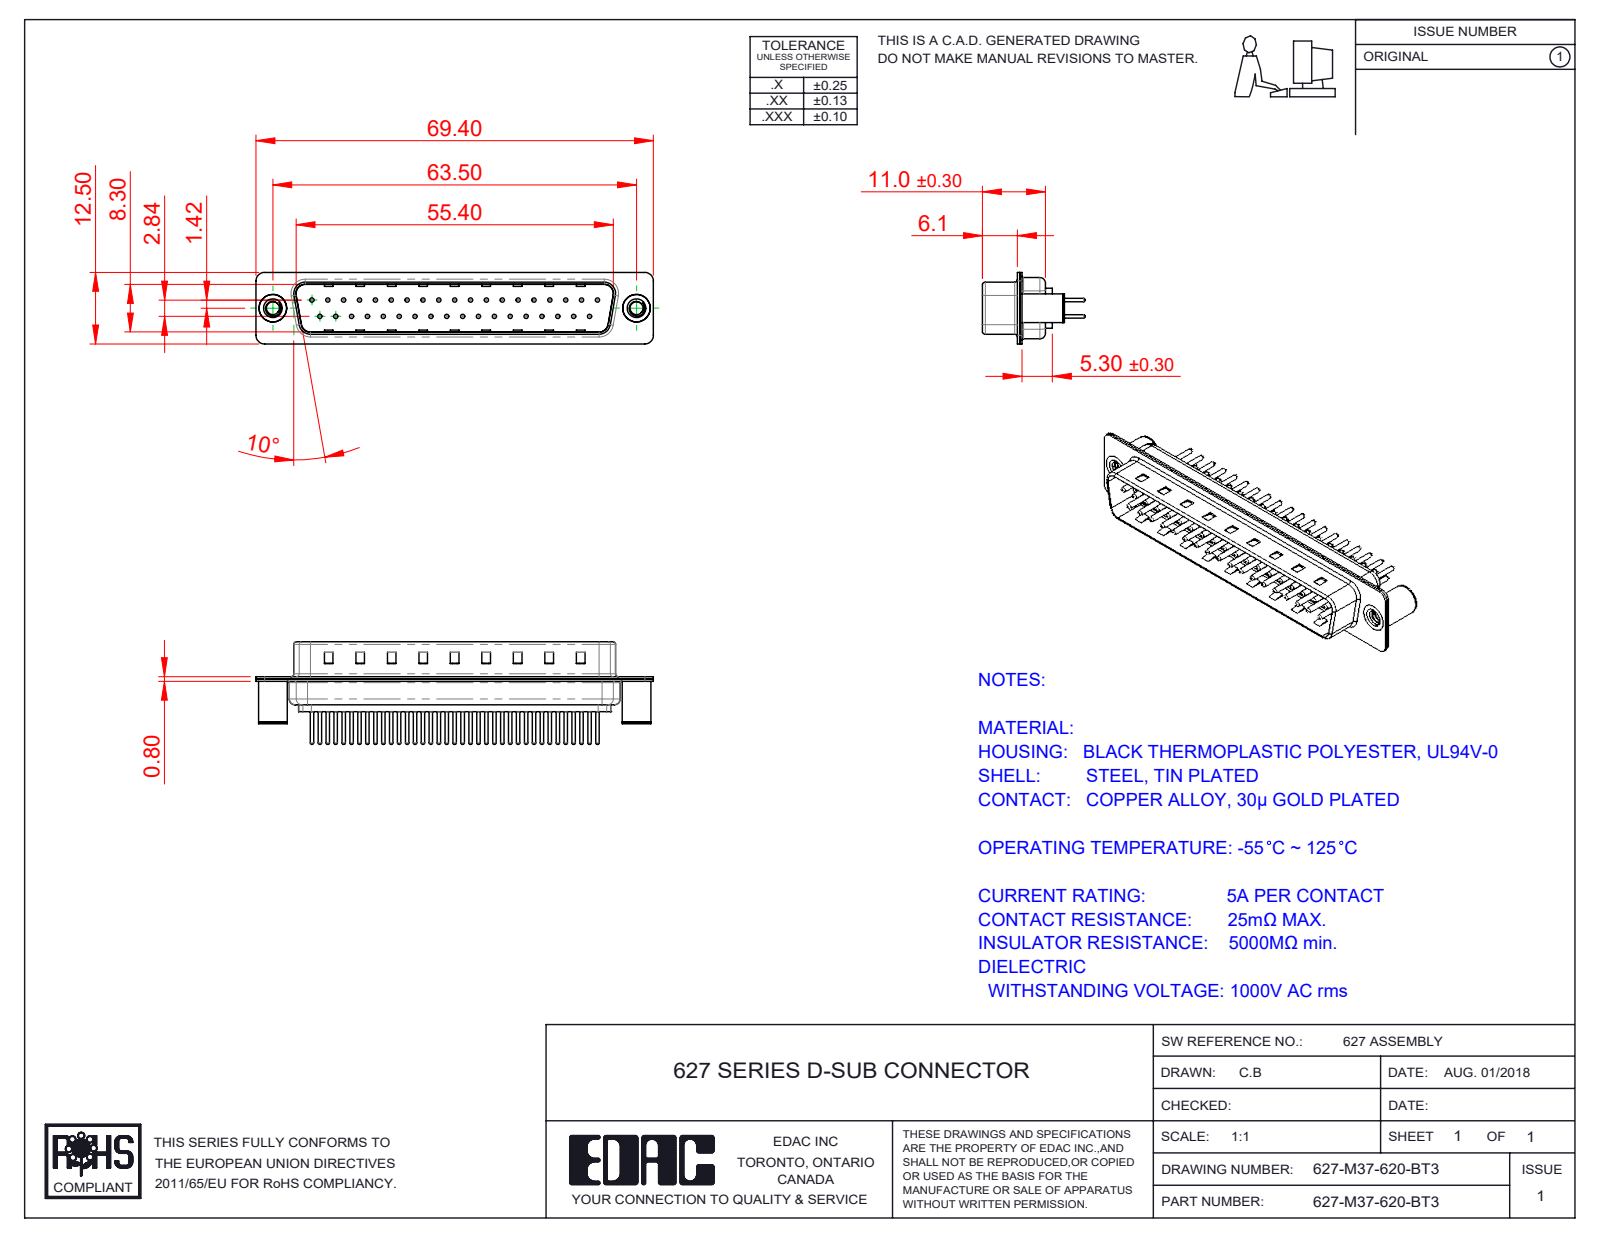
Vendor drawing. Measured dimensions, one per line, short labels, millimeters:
name: 627M Shell Rear_37 Contacts; 627M 4-40 Threaded Board Spacer; 627M Shell Front_37 Contacts; 627-M37-620-BT3 (+3 more)
written by: SolidWorks 2020 (CONFIG_CONTROL_DESIGN)
unit: mm
bodies: 42 solids, 1815 faces (462 planar, 683 cylindrical, 670 other)
size: 69.4 × 17.9 × 12.5
volume: 3 891 mm³; area: 9 528 mm²
holes: 37× ⌀0.75, 37× ⌀1.6, 37× ⌀2, 2× ⌀2.26, 2× ⌀3.26, 2× ⌀4, 2× ⌀4.8
bosses: 37× ⌀1.5, 37× ⌀0.6, 2× ⌀5, 2× ⌀4.9
rounds: 16× R1.5, 12× R2, 8× R0.5, 8× R1.6, 4× R0.25, 4× R0.6, 4× R0.65, 4× R0.9
face distances: 0.4, 0.8, 9.5, 9.1, 8.7, 9.9, 1.2, 5.7, 0.75, 0.35
hole spacings: 2.77, 5.54, 3.16, 8.31, 11.08, 13.85, 16.62, 19.39
